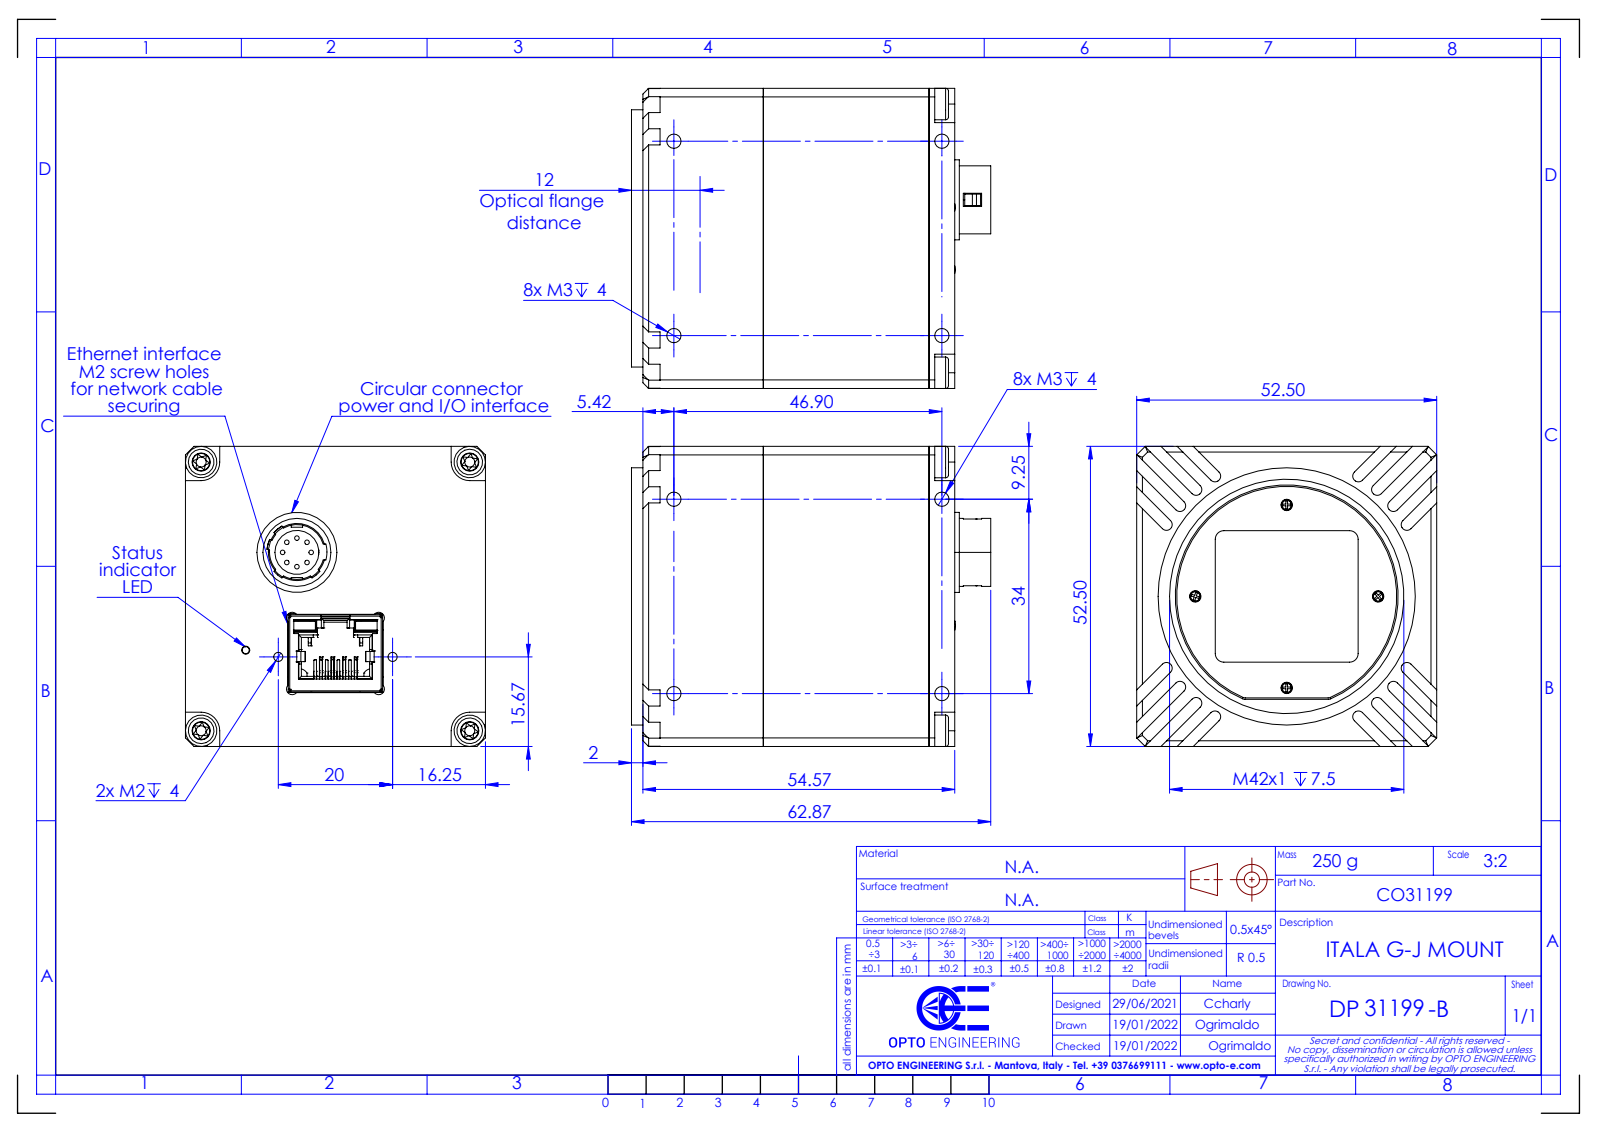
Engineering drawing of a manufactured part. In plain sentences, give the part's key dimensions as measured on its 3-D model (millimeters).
The part is named "DP31199-B_ITALA G-J MOUNT". Its 3-D file was written by "SolidWorks 2021 (CONFIG_CONTROL_DESIGN)". It is 0 solids with 711 faces: 474 planar, 183 cylindrical and 54 other. Overall it measures 62.87 by 52.5 by 52.5 millimeters. Round holes: 8 of diameter 2.5, 2 of diameter 1.6, 1 of diameter 7.7, 1 of diameter 10, 1 of diameter 39, 1 of diameter 41. Round bosses or shafts: 8 of diameter 0.8, 4 of diameter 5.5, 1 of diameter 45, 1 of diameter 14, 1 of diameter 11.9, 1 of diameter 1.45. Partial cylindrical surfaces (rounded edges, fillets, slot ends): 20 of radius 1, 6 of radius 0.25, 6 of radius 1.5, 4 of radius 3.25, 2 of radius 0.75, 2 of radius 1.14, 2 of radius 5.25, 1 of radius 0.6. The main face-to-face distances are 52.5, 48.55, 2, 41.91, 6.64, 6.02, 47.93, 54.57, 4, 0.5. The hole center spacings are 34, 46.9, 57.93, 14.56, 10.24, 18.57, 20, 24.79.
